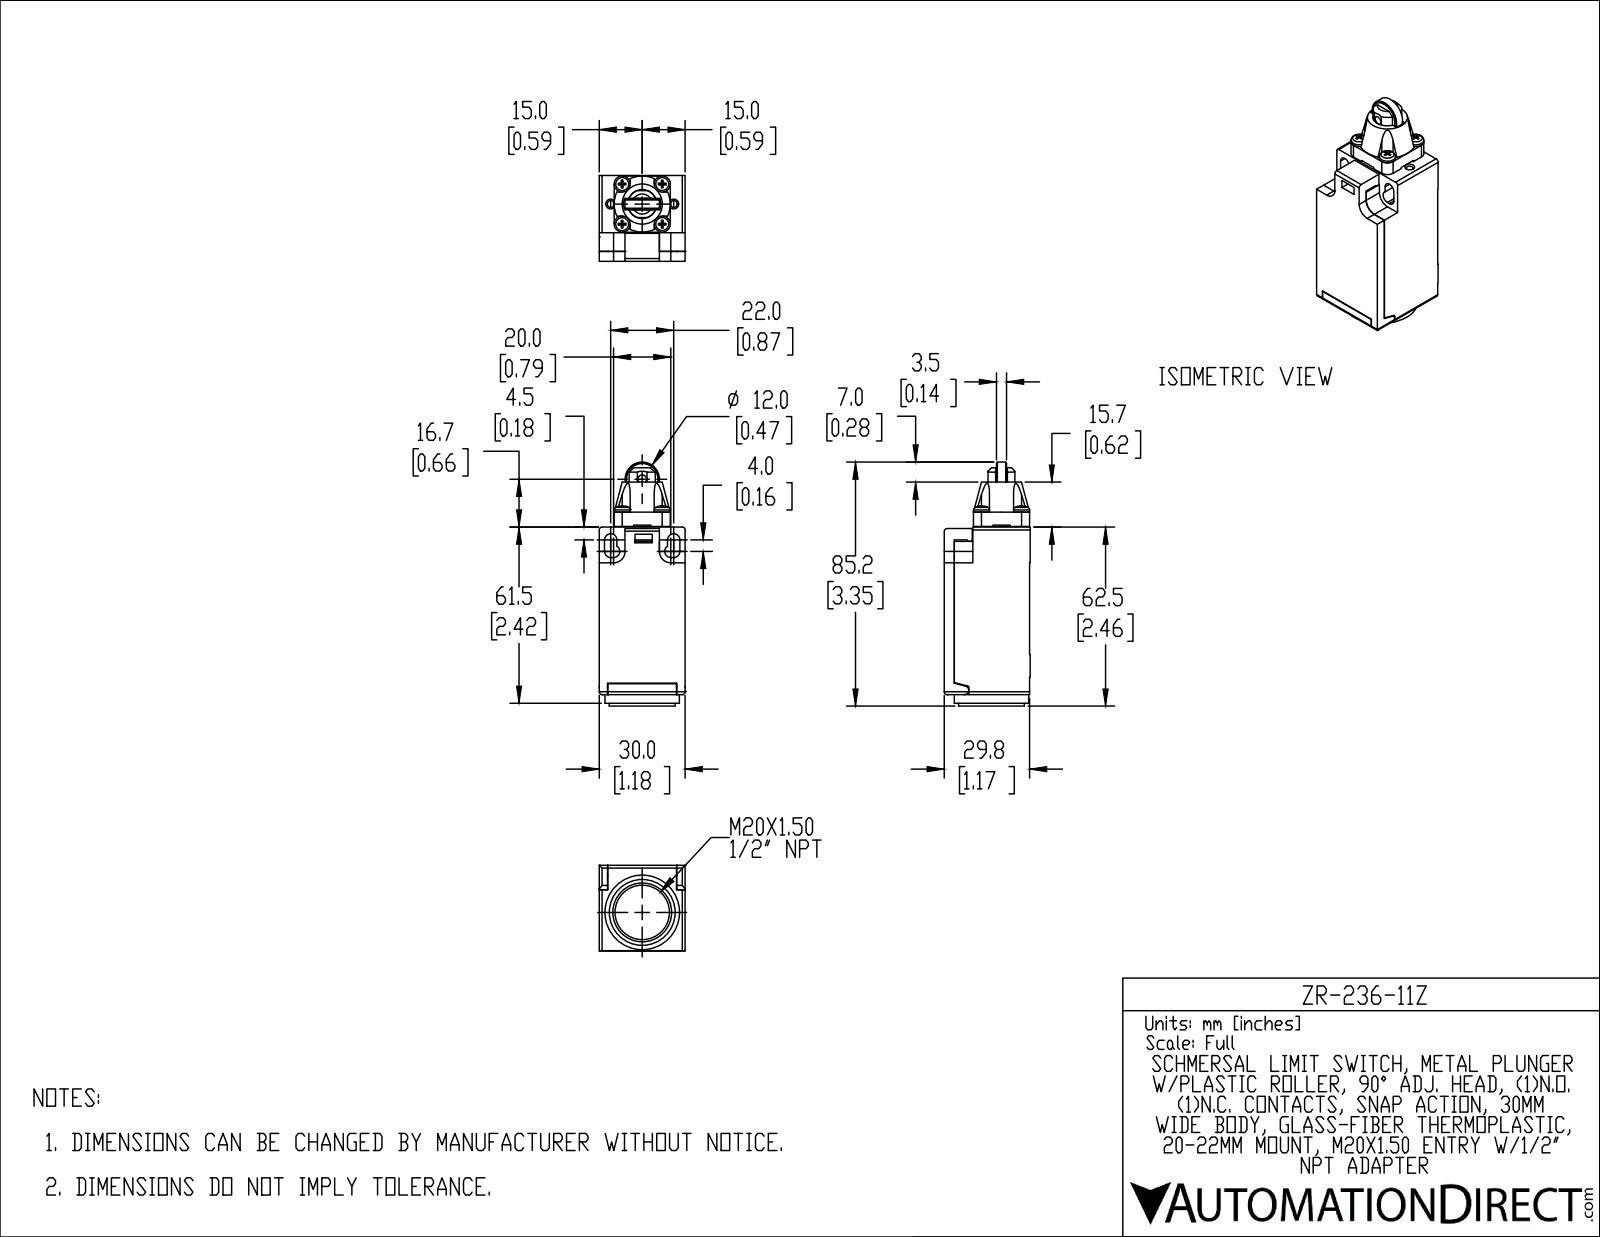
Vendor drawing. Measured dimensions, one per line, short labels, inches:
name: ZR-236-11Z
written by: SolidWorks 2019 (AUTOMOTIVE_DESIGN)
unit: in
bodies: 3 solids, 322 faces (230 planar, 72 cylindrical, 20 other)
size: 3.354 × 1.181 × 1.181
volume: 3.129 in³; area: 27.03 in²
holes: 6× ⌀0.094, 4× ⌀0.126, 1× ⌀0.118, 1× ⌀0.512, 1× ⌀0.545, 1× ⌀0.748
bosses: 4× ⌀0.213, 2× ⌀0.221, 1× ⌀1.024, 1× ⌀0.906, 1× ⌀0.472, 1× ⌀0.415, 1× ⌀0.276, 1× ⌀0.248
rounds: 8× R0.11, 6× R0.039, 6× R0.085, 2× R0.11, 2× R0.157, 1× R0.024, 1× R0.059, 1× R0.197
face distances: 1.181, 0.138, 1.035, 1.173, 1.043, 0.157, 2.067, 0.118, 0.236, 0.394
hole spacings: 0.317, 0.39, 0.551, 0.76, 0.308, 0.433, 0.454, 0.497
